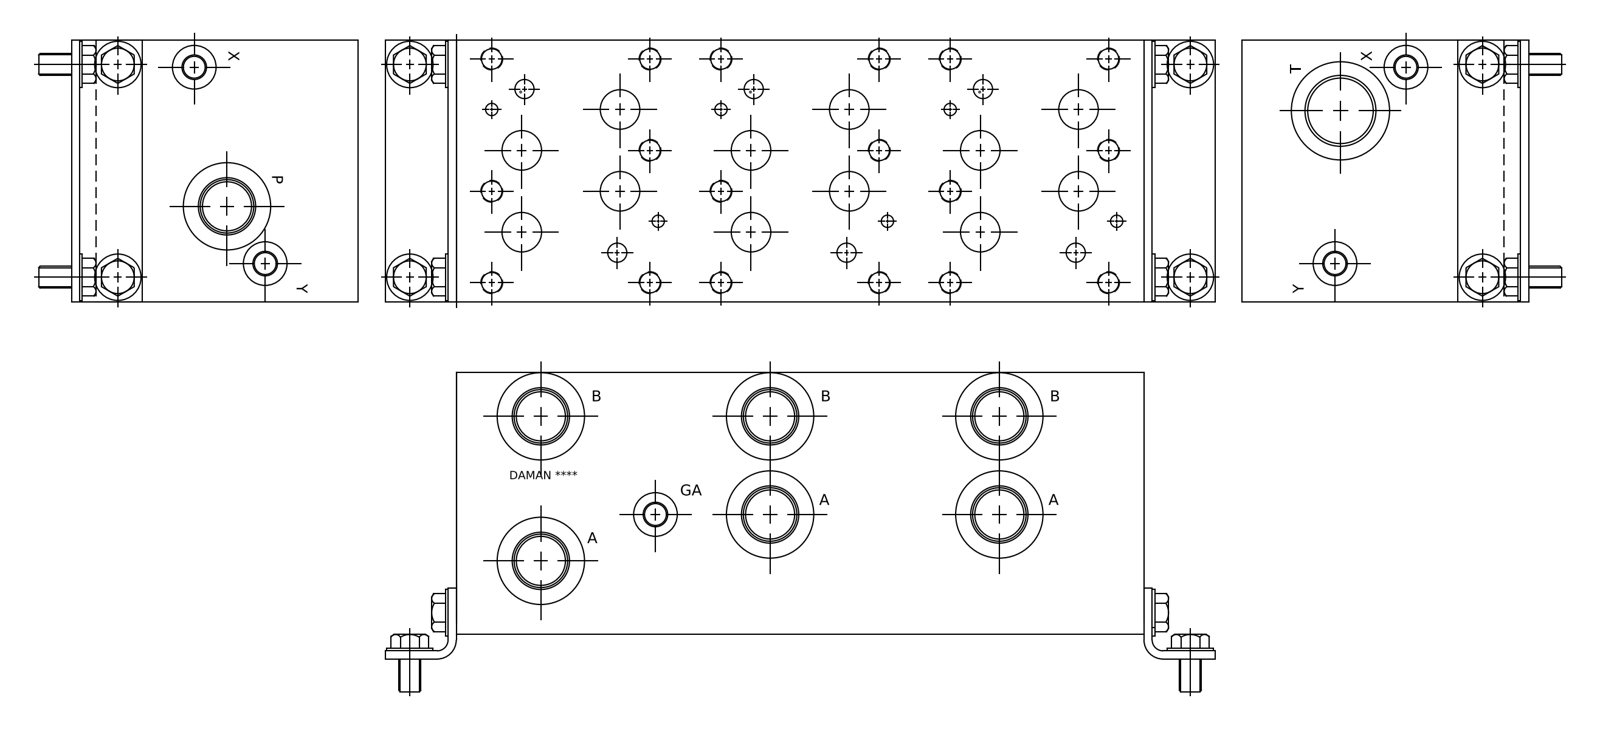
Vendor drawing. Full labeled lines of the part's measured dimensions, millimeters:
Part name (STEP PRODUCT): Part_AD08S035S_3D
STEP written by: Autodesk Inventor 2019 (AUTOMOTIVE_DESIGN)
Units: millimetres
Bodies: 1 solid, 859 faces (418 planar, 142 cylindrical, 299 other)
Overall size (bounding box): 400.05 × 152.4 × 152.4
Volume: 8 869 000 mm³ · Surface area: 364 462 mm²
Round holes (diameter × count): ⌀10.72 ×21, ⌀12.7 ×21, ⌀23.01 ×12, ⌀11.13 ×7, ⌀28.57 ×7, ⌀31.27 ×7, ⌀33.76 ×7, ⌀49.12 ×7, ⌀7.14 ×6, ⌀33.35 ×5, ⌀35.51 ×5, ⌀14.27 ×3
Main face-to-face distances: 152.4, 400.05, 0.79, 151.61, 399.26, 398.47, 19.84, 19.05, 122.17, 30.23
Hole centre spacings: 133.35, 61.92, 152.7, 191.98, 266.7, 29.53, 74.63, 58.72
